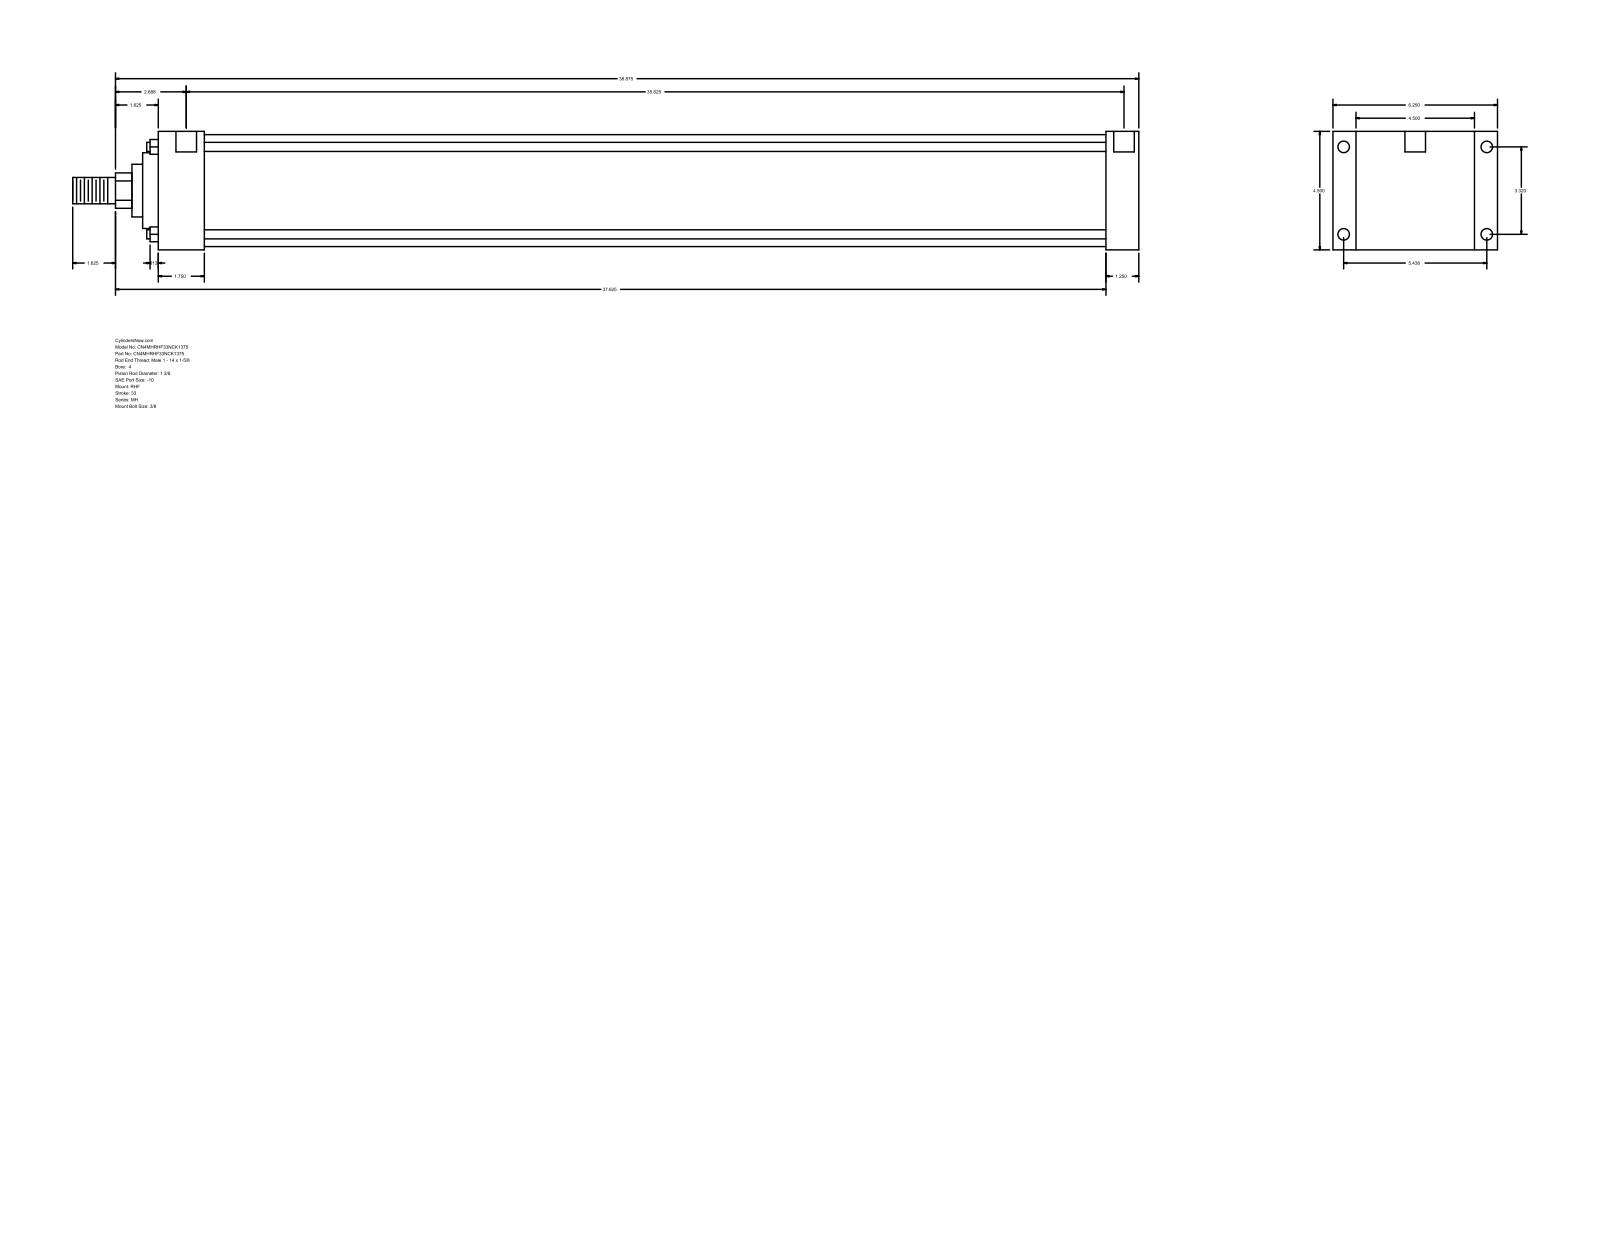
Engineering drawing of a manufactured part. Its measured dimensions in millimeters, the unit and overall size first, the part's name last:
Units: millimetres
Overall size (bounding box): 1028.7 × 158.75 × 114.3
Round holes (diameter × count): ⌀8.73 ×4, ⌀11.13 ×4, ⌀19.84 ×2
Round bosses / shafts (diameter × count): ⌀8.76 ×4, ⌀107.95 ×1, ⌀73.03 ×1, ⌀50.8 ×1, ⌀34.92 ×1, ⌀25.4 ×1
Partial cylindrical surfaces — rounded edges, fillets, slot ends (radius × count): R17.06 ×1
Main face-to-face distances: 114.3, 31.75, 914.4, 946.15, 22.23, 136.53, 44.45, 869.95, 901.7, 158.76
Hole centre spacings: 1.59, 84.32, 138.12, 161.82, 906.47, 908.06, 904.88
Bodies: 0 solids, 90 faces (61 planar, 29 cylindrical, 0 other)
Part name (STEP PRODUCT): MH_RHF__0400_1.375
STEP written by: GSSL Pune (CONFIG_CONTROL_DESIGN)
